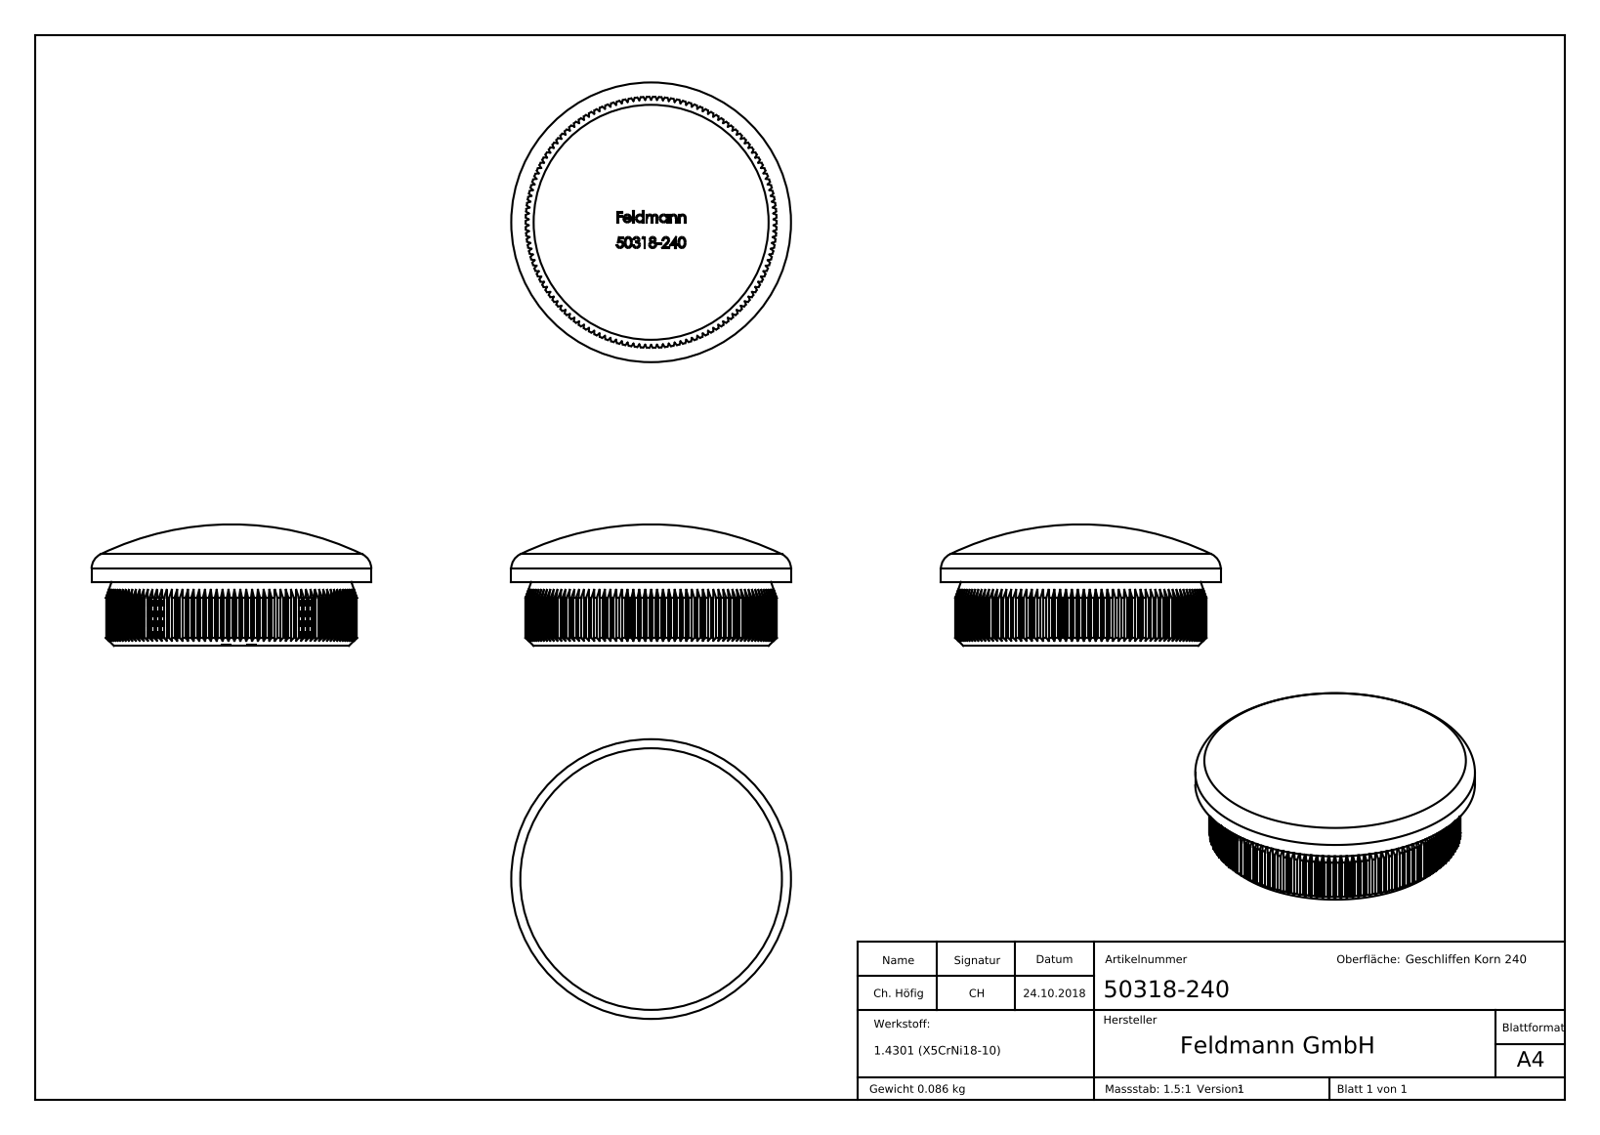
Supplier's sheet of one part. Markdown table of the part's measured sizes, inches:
| quantity | value |
| --- | --- |
| part name | 50318-240 |
| STEP written by | SolidWorks 2015 (CONFIG_CONTROL_DESIGN) |
| units | inches |
| bodies | 1 solid, 624 faces (381 planar, 132 cylindrical, 111 other) |
| overall size | 1.378 × 1.378 × 0.598 |
| volume | 0.665 in³ |
| surface area | 5.236 in² |
| round bosses / shafts (diameter × count) | 1.378 × 1 |
| partial cylindrical surfaces (radius × count) | 0.618 × 1 |
| main face-to-face distances | 0.315, 0.605, 0.604, 0.311, 0.117, 0.015, 0.055, 0.133, 0.126, 0.144 |
